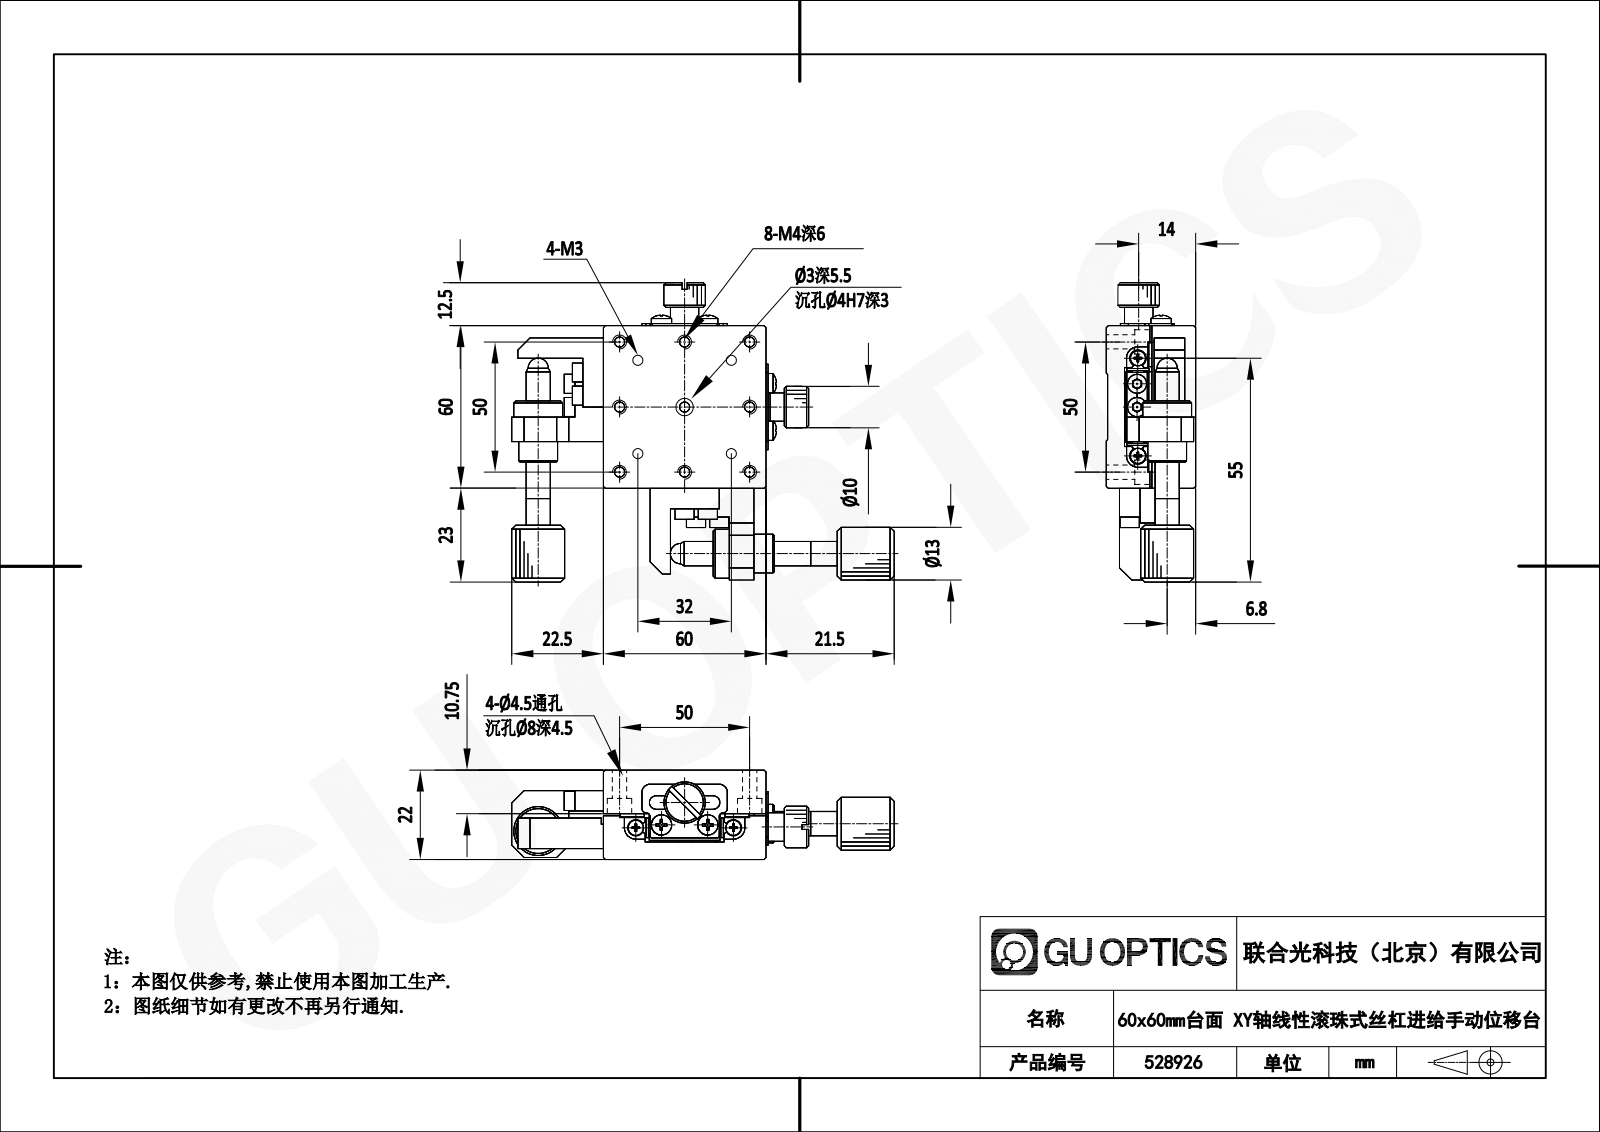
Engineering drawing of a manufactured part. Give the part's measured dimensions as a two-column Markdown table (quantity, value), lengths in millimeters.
| quantity | value |
| --- | --- |
| part name | 528926 |
| STEP written by | SolidWorks 2020 (CONFIG_CONTROL_DESIGN) |
| units | millimeters |
| bodies | 0 solids, 1421 faces (717 planar, 380 cylindrical, 324 other) |
| overall size | 105 × 94.5 × 22 |
| round holes (diameter × count) | 2.05 × 4, 2.5 × 4, 2.8 × 4, 3 × 4, 7 × 1 |
| round bosses / shafts (diameter × count) | 3.24 × 8, 2.05 × 6, 2.5 × 5, 6 × 4, 4.5 × 4, 2.46 × 4, 12 × 2, 9.5 × 2 |
| partial cylindrical surfaces (radius × count) | 2 × 8, 0.5 × 4, 1 × 4, 1.65 × 4, 5 × 2, 6.5 × 2 |
| main face-to-face distances | 5.7, 16.3, 0.5, 60, 5.5, 10.8, 4.6, 10.6, 10.1, 6.2 |
| hole center spacings | 6, 12, 8.14, 8.73, 10.59, 13.79, 5.5, 5.7 |
